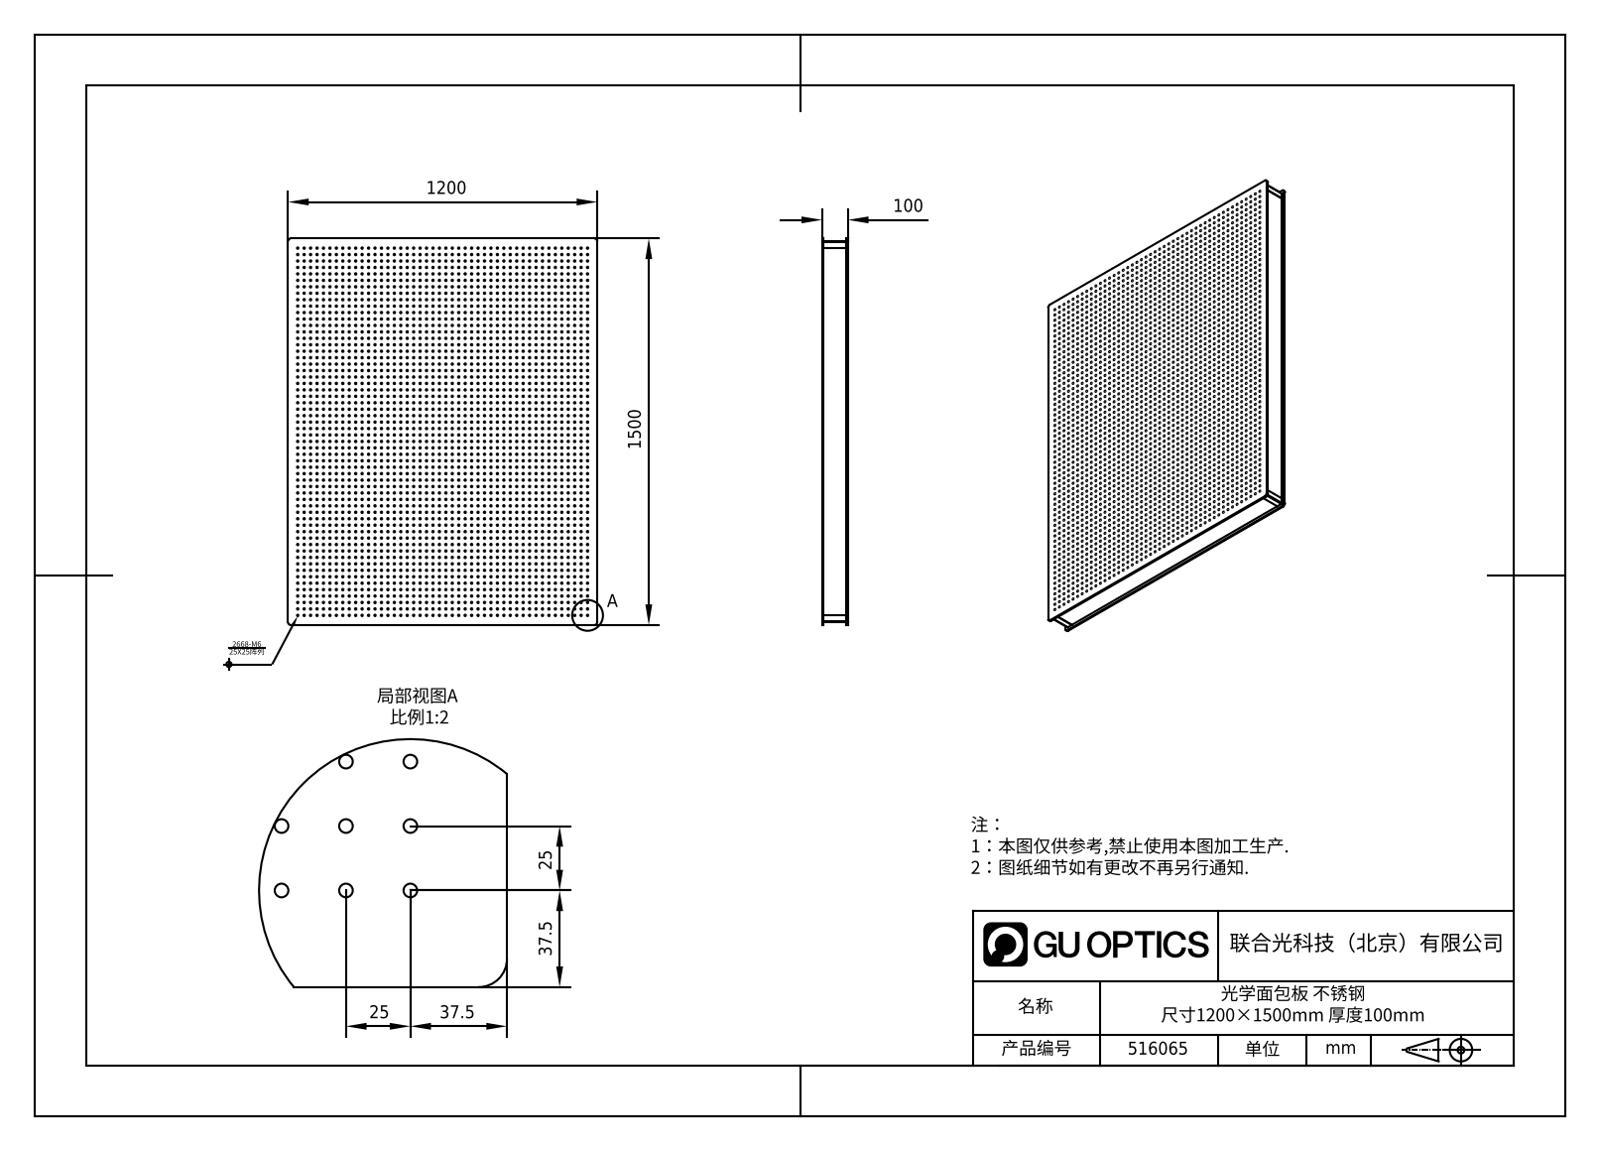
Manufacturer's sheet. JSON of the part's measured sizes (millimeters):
{"part_name": "516065", "step_written_by": "SolidWorks 2020 (CONFIG_CONTROL_DESIGN)", "units": "millimeters", "bodies": {"solids": 1, "faces": 8064, "planar": 2712, "cylindrical": 5352, "other": 0}, "overall_size": [1500, 1200, 100], "volume_mm3": 173500000, "surface_area_mm2": 4554000, "round_holes": [[5.3, 2668]], "partial_cylinders_radius": [[2, 4], [3, 4], [11, 4]], "face_to_face_distances": [100, 1174, 6, 94, 1474, 95, 89, 5, 13, 1187], "hole_center_spacings": [79.06, 35.36, 50, 127.48, 70.71, 176.78, 100, 111.8]}
